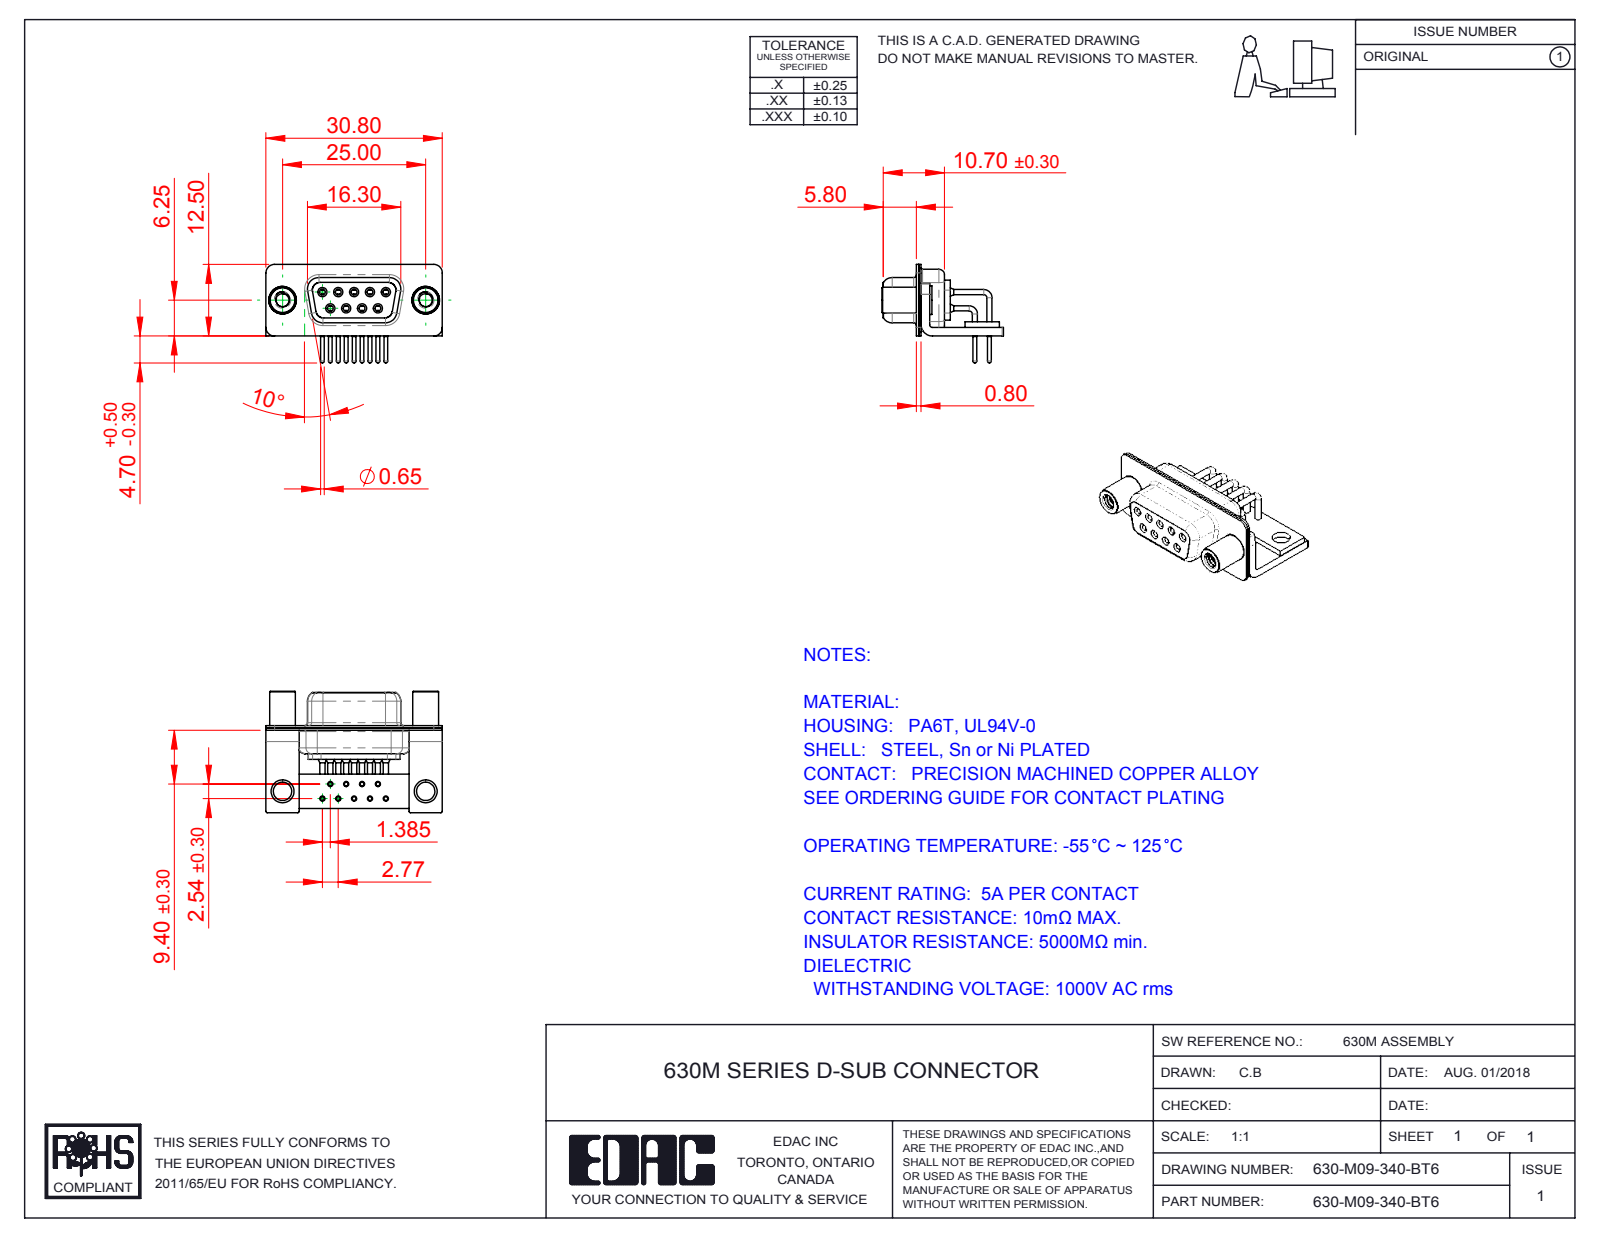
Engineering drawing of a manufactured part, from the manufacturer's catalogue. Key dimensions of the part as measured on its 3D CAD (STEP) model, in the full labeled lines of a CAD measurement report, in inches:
Part name (STEP PRODUCT): 630M Shell Rear_09 Contacts; 630-M09-340-BT6; 630M Contact Row 2; 630M Housing_09 Contacts (+5 more)
STEP written by: SolidWorks 2016 (CONFIG_CONTROL_DESIGN)
Units: inches
Bodies: 17 solids, 874 faces (230 planar, 426 cylindrical, 218 other)
Overall size (bounding box): 1.213 × 0.835 × 0.677
Volume: 0.141 in³ · Surface area: 9.292 in²
Round holes (diameter × count): ⌀0.035 ×9, ⌀0.039 ×9, ⌀0.043 ×9, ⌀0.067 ×9, ⌀0.071 ×9, ⌀0.079 ×9, ⌀0.089 ×2, ⌀0.126 ×2, ⌀0.157 ×2, ⌀0.189 ×2
Round bosses / shafts (diameter × count): ⌀0.063 ×9, ⌀0.059 ×9, ⌀0.035 ×9, ⌀0.026 ×9, ⌀0.197 ×2, ⌀0.193 ×2, ⌀0.177 ×2
Partial cylindrical surfaces — rounded edges, fillets, slot ends (radius × count): R0.01 ×16, R0.059 ×16, R0.079 ×13, R0.053 ×8, R0.063 ×8, R0.02 ×5, R0.024 ×4, R0.026 ×4
Main face-to-face distances: 0.016, 0.031, 0.059, 0.091, 0.075, 0.039, 0.368, 0.057, 0.335, 0.352
Hole centre spacings: 0.109, 0.218, 0.124, 0.192, 0.327, 0.114, 0.114, 0.198
